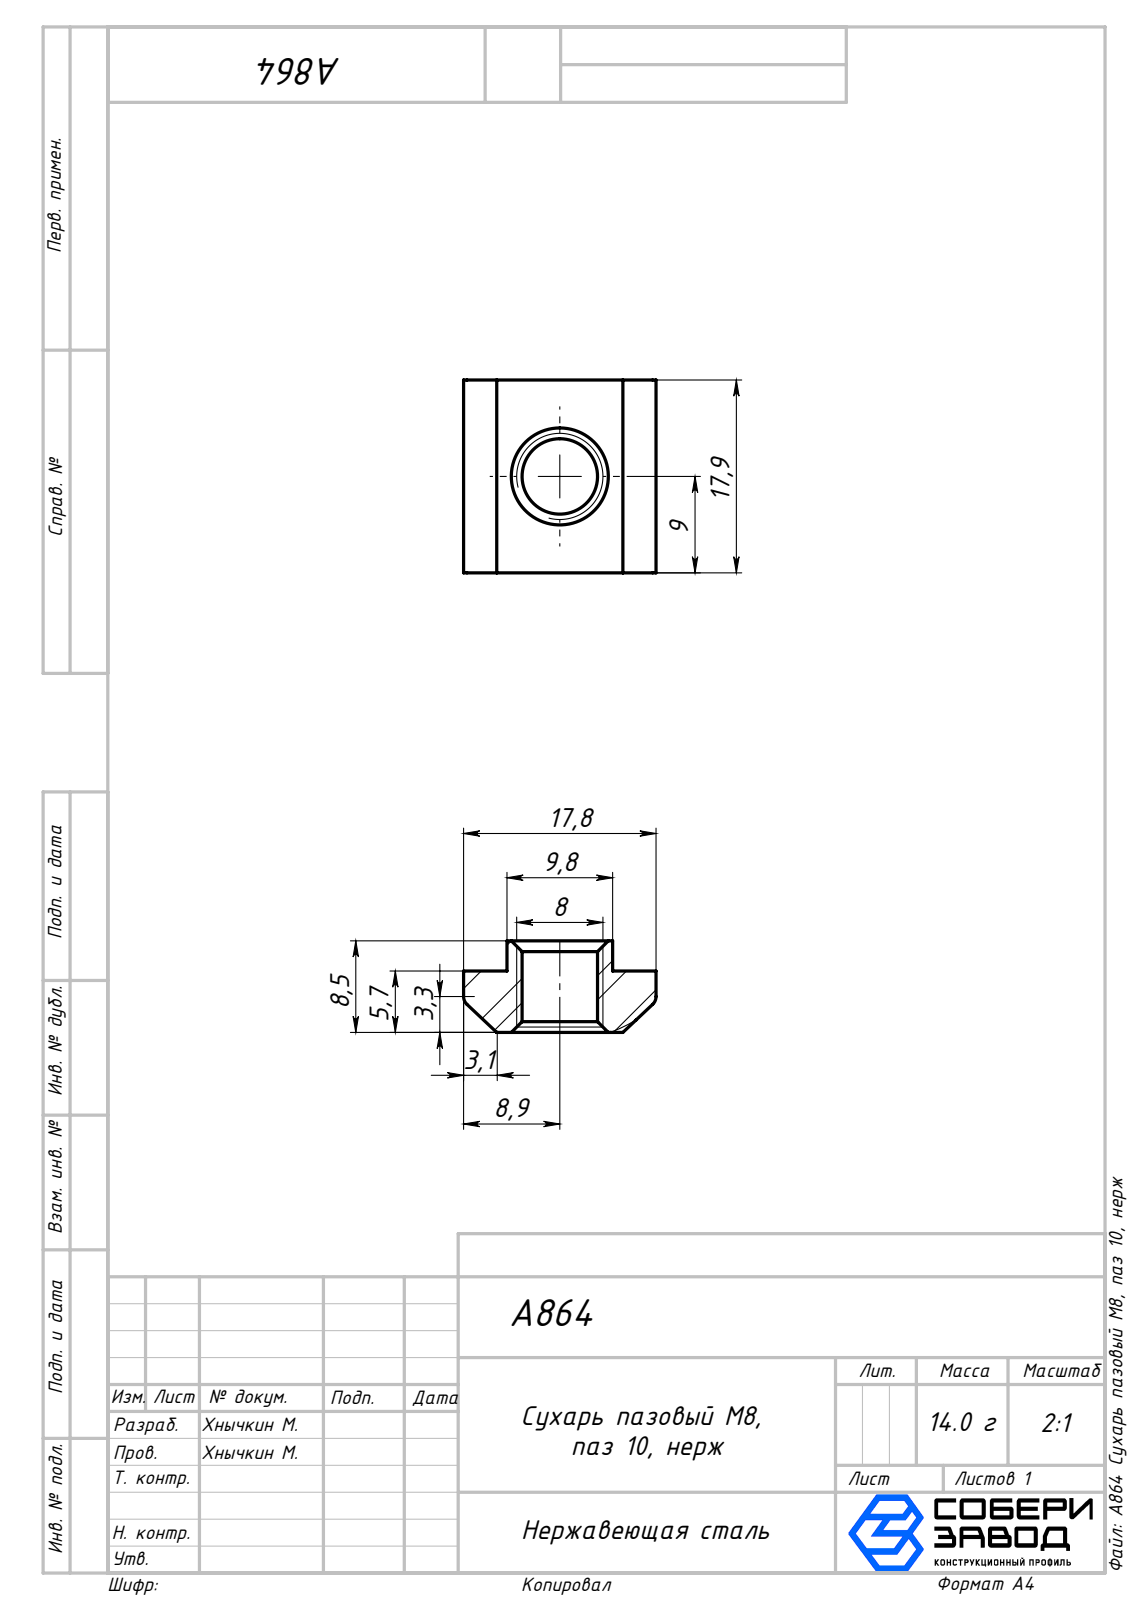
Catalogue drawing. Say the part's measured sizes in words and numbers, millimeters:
The part is named "A864 Сухарь пазовый М8, паз 10, нерж". Its 3-D file was written by "SolidWorks 2025 (AUTOMOTIVE_DESIGN)". It is 1 solid with 20 faces: 12 planar, 4 cylindrical and 4 other. Overall it measures 17.9 by 17.85 by 8.5 millimeters. Its volume is 1 801 cubic millimeters and its surface area 1 206 square millimeters. Round holes: 1 of diameter 7. Partial cylindrical surfaces (rounded edges, fillets, slot ends): 2 of radius 1. The main face-to-face distances are 5.7, 17.9, 8.5, 2.8, 4.03, 13.83, 9.8, 17.86.
